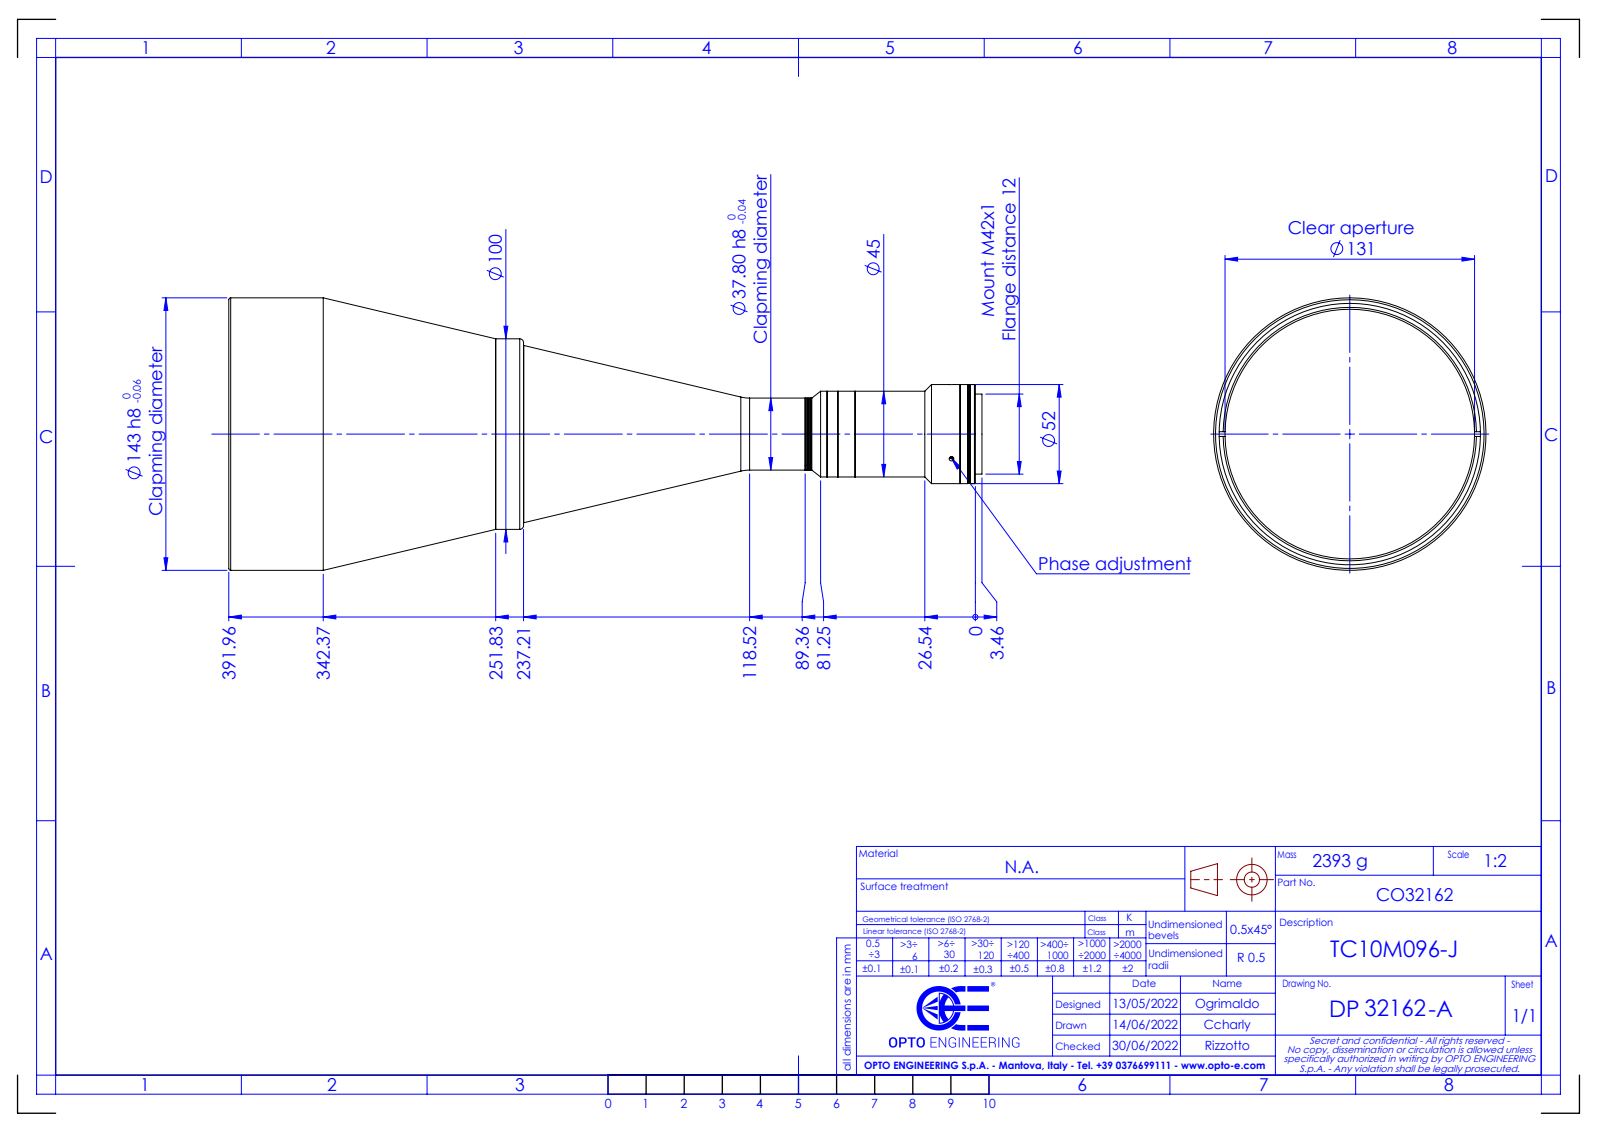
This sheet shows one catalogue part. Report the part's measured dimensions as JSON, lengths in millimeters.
{"part_name": "DP32162-A_TC10M096-J", "step_written_by": "SolidWorks 2021 (CONFIG_CONTROL_DESIGN)", "units": "millimeters", "bodies": {"solids": 0, "faces": 102, "planar": 26, "cylindrical": 52, "other": 24}, "overall_size": [395.42, 143, 143], "round_holes": [[2.5, 3], [38, 1], [131, 1], [137.2, 1]], "round_bosses_or_shafts": [[143, 1], [100, 1], [93, 1], [52, 1], [51.8, 1], [45, 1], [42, 1], [37.8, 1]], "face_to_face_distances": [139.41, 388.68, 249.27, 0.72, 140.13, 389.4, 387.92, 387.2, 247.79, 1.48]}
